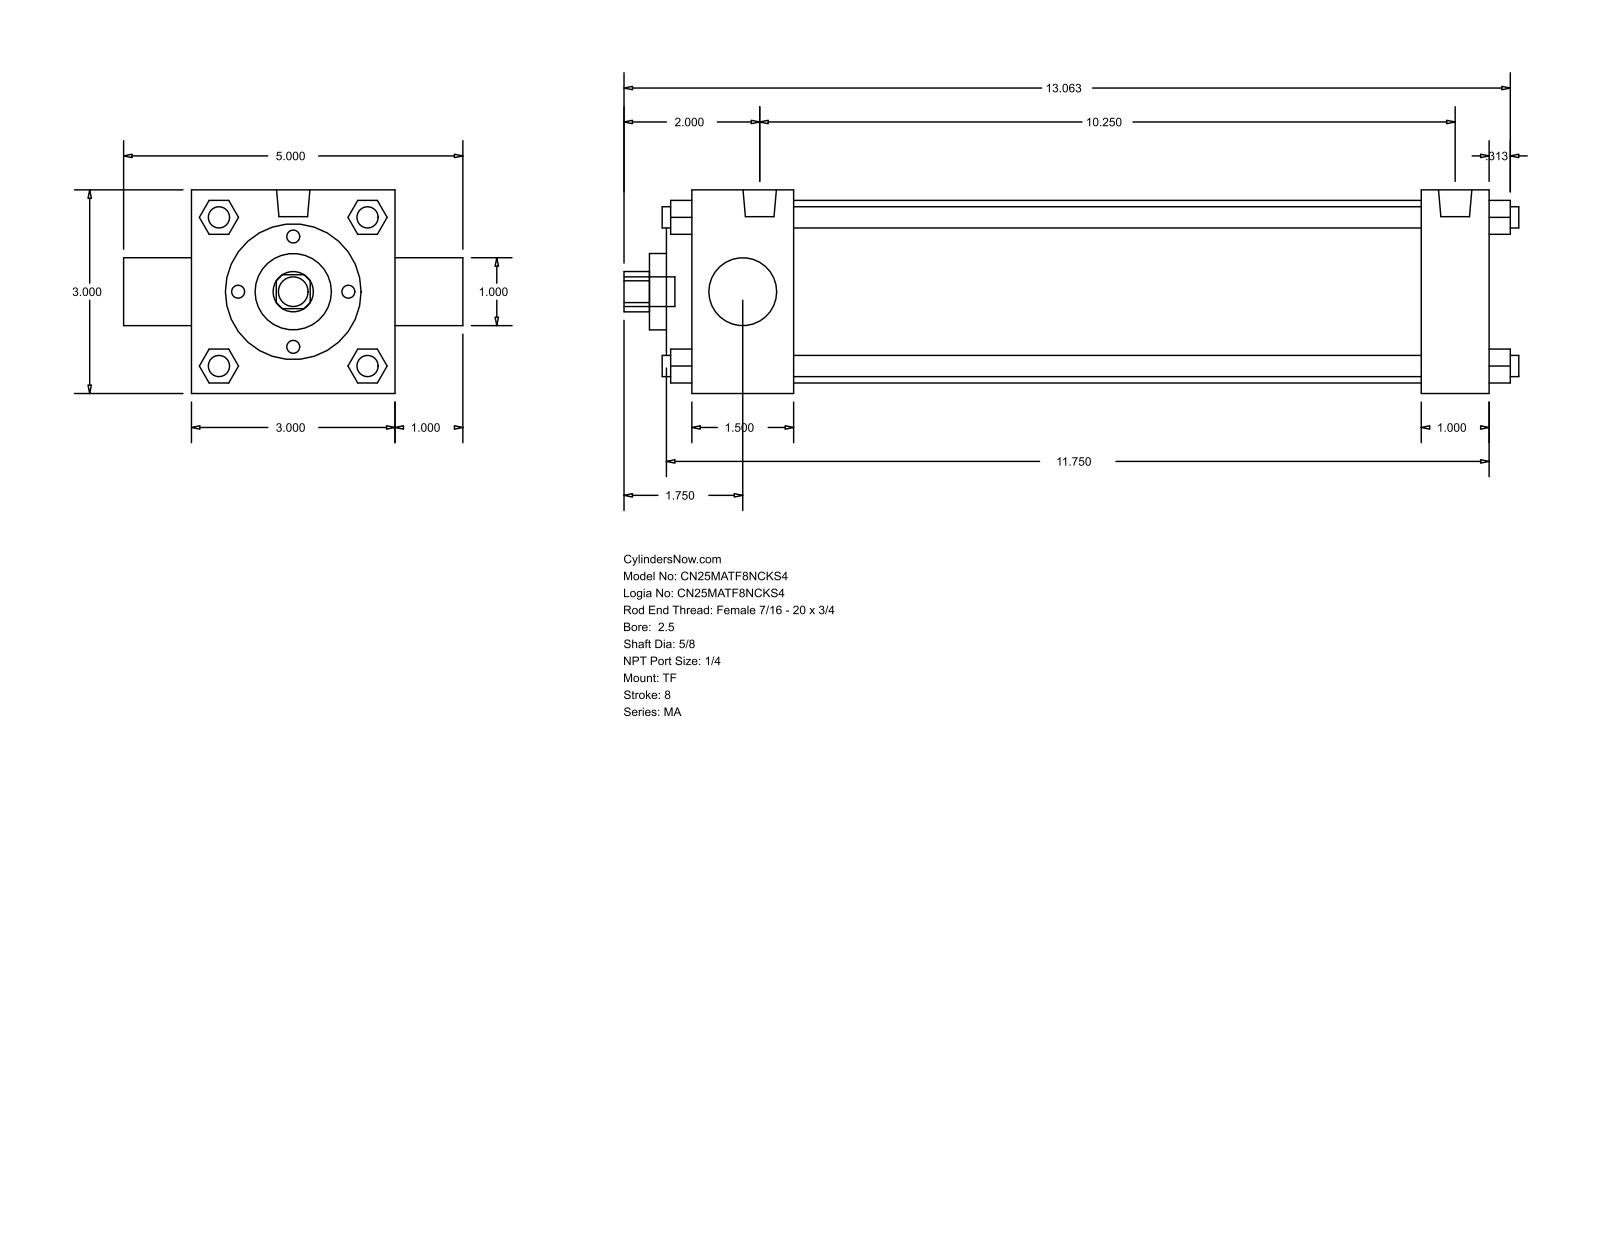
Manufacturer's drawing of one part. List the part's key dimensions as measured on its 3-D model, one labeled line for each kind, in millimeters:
Part name (STEP PRODUCT): MA_TF__0250_0.625
STEP written by: GSSL Pune (CONFIG_CONTROL_DESIGN)
Units: millimetres
Bodies: 0 solids, 122 faces (93 planar, 29 cylindrical, 0 other)
Overall size (bounding box): 334.96 × 127 × 76.2
Round holes (diameter × count): ⌀15.88 ×1, ⌀25.4 ×1, ⌀28.57 ×1, ⌀50.8 ×1, ⌀68.33 ×1
Round bosses / shafts (diameter × count): ⌀7.94 ×7, ⌀12.49 ×2, ⌀11.11 ×1
Partial cylindrical surfaces — rounded edges, fillets, slot ends (radius × count): R7.54 ×1
Main face-to-face distances: 76.2, 298.45, 25.4, 38.1, 273.05, 234.95, 260.35, 12.7, 9.52, 47.62
